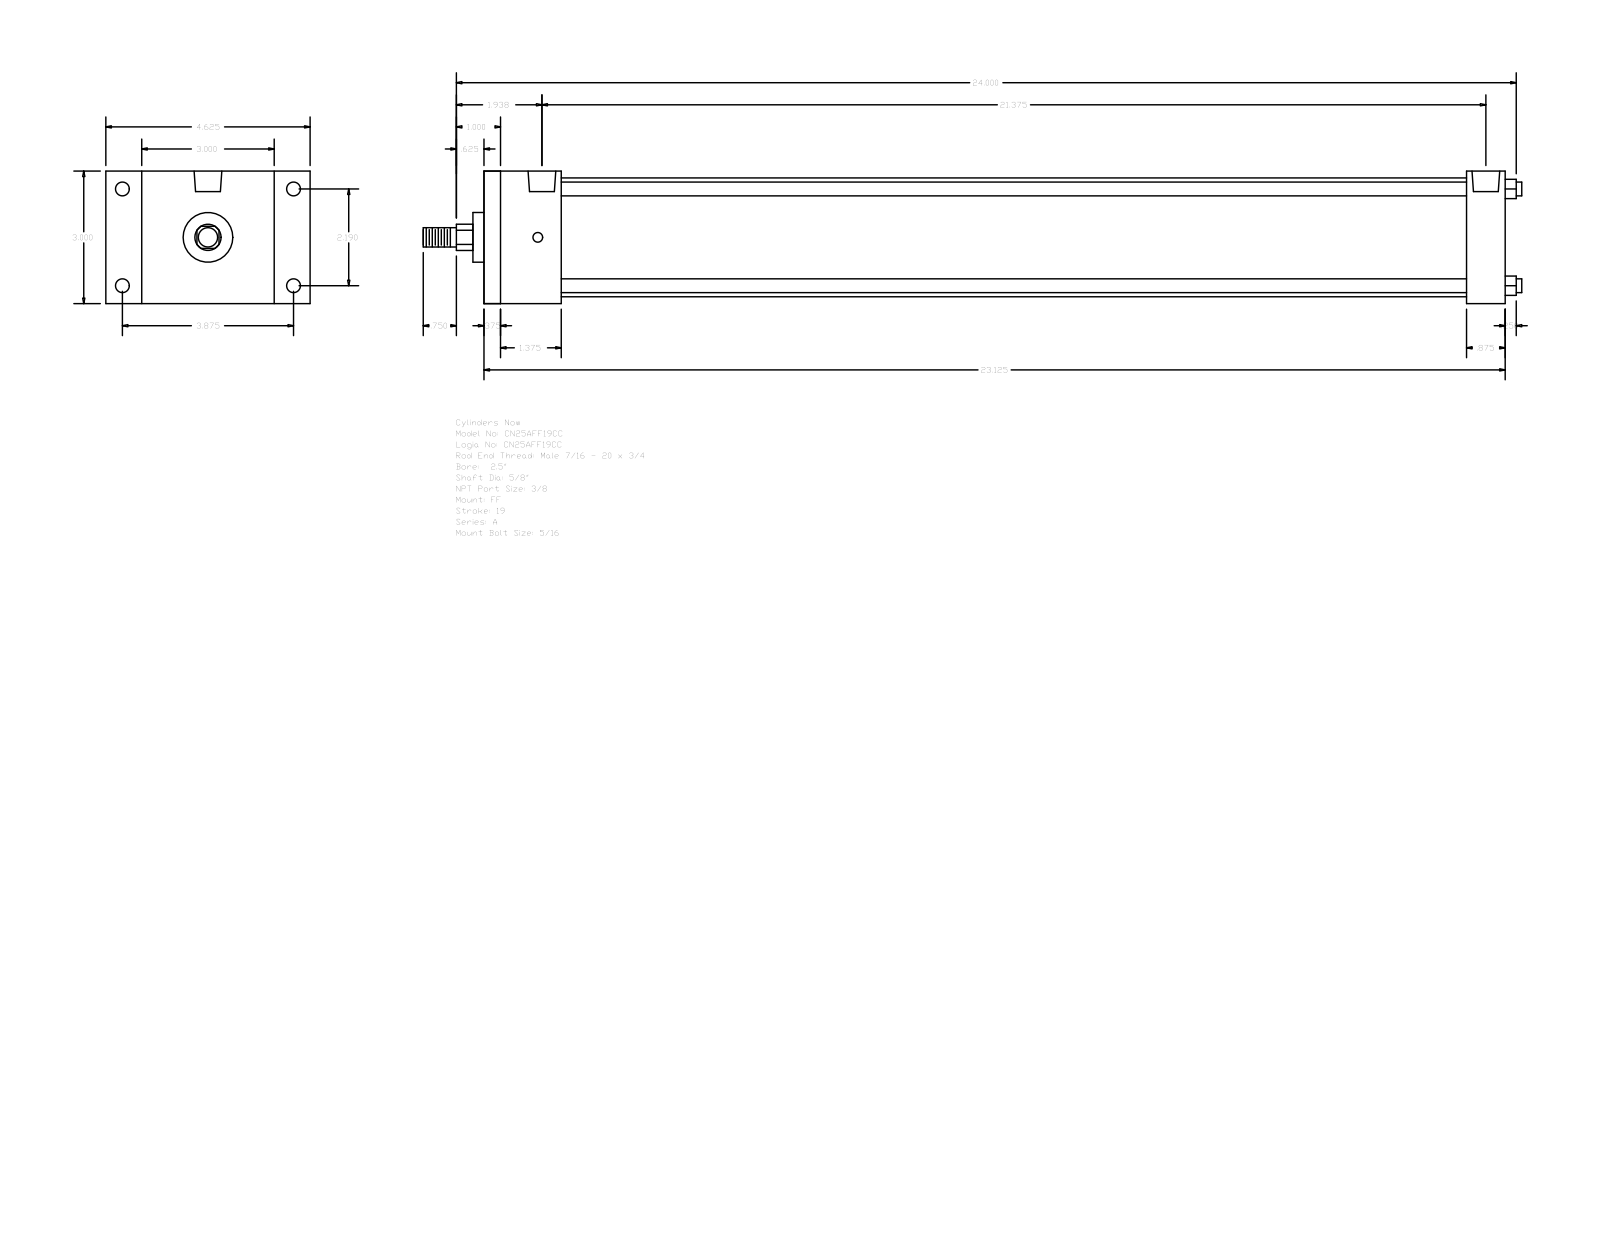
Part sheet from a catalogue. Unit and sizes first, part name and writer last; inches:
Units: inches
Overall size (bounding box): 24.875 × 4.625 × 3
Round holes (diameter × count): ⌀0.219 ×4, ⌀0.313 ×4, ⌀0.627 ×2
Round bosses / shafts (diameter × count): ⌀0.313 ×4, ⌀2.69 ×1, ⌀1.125 ×1, ⌀0.625 ×1, ⌀0.437 ×1
Partial cylindrical surfaces — rounded edges, fillets, slot ends (radius × count): R0.297 ×1
Main face-to-face distances: 3, 23.125, 0.375, 22.75, 1.75, 1.375, 22.25, 21.875, 20.5, 21.375
Hole centre spacings: 0.094, 2.19, 3.875, 4.451, 21.469, 21.563, 21.375
Bodies: 0 solids, 92 faces (64 planar, 28 cylindrical, 0 other)
Part name (STEP PRODUCT): A_FF__0250_0.625
STEP written by: GSSL Pune (CONFIG_CONTROL_DESIGN)
